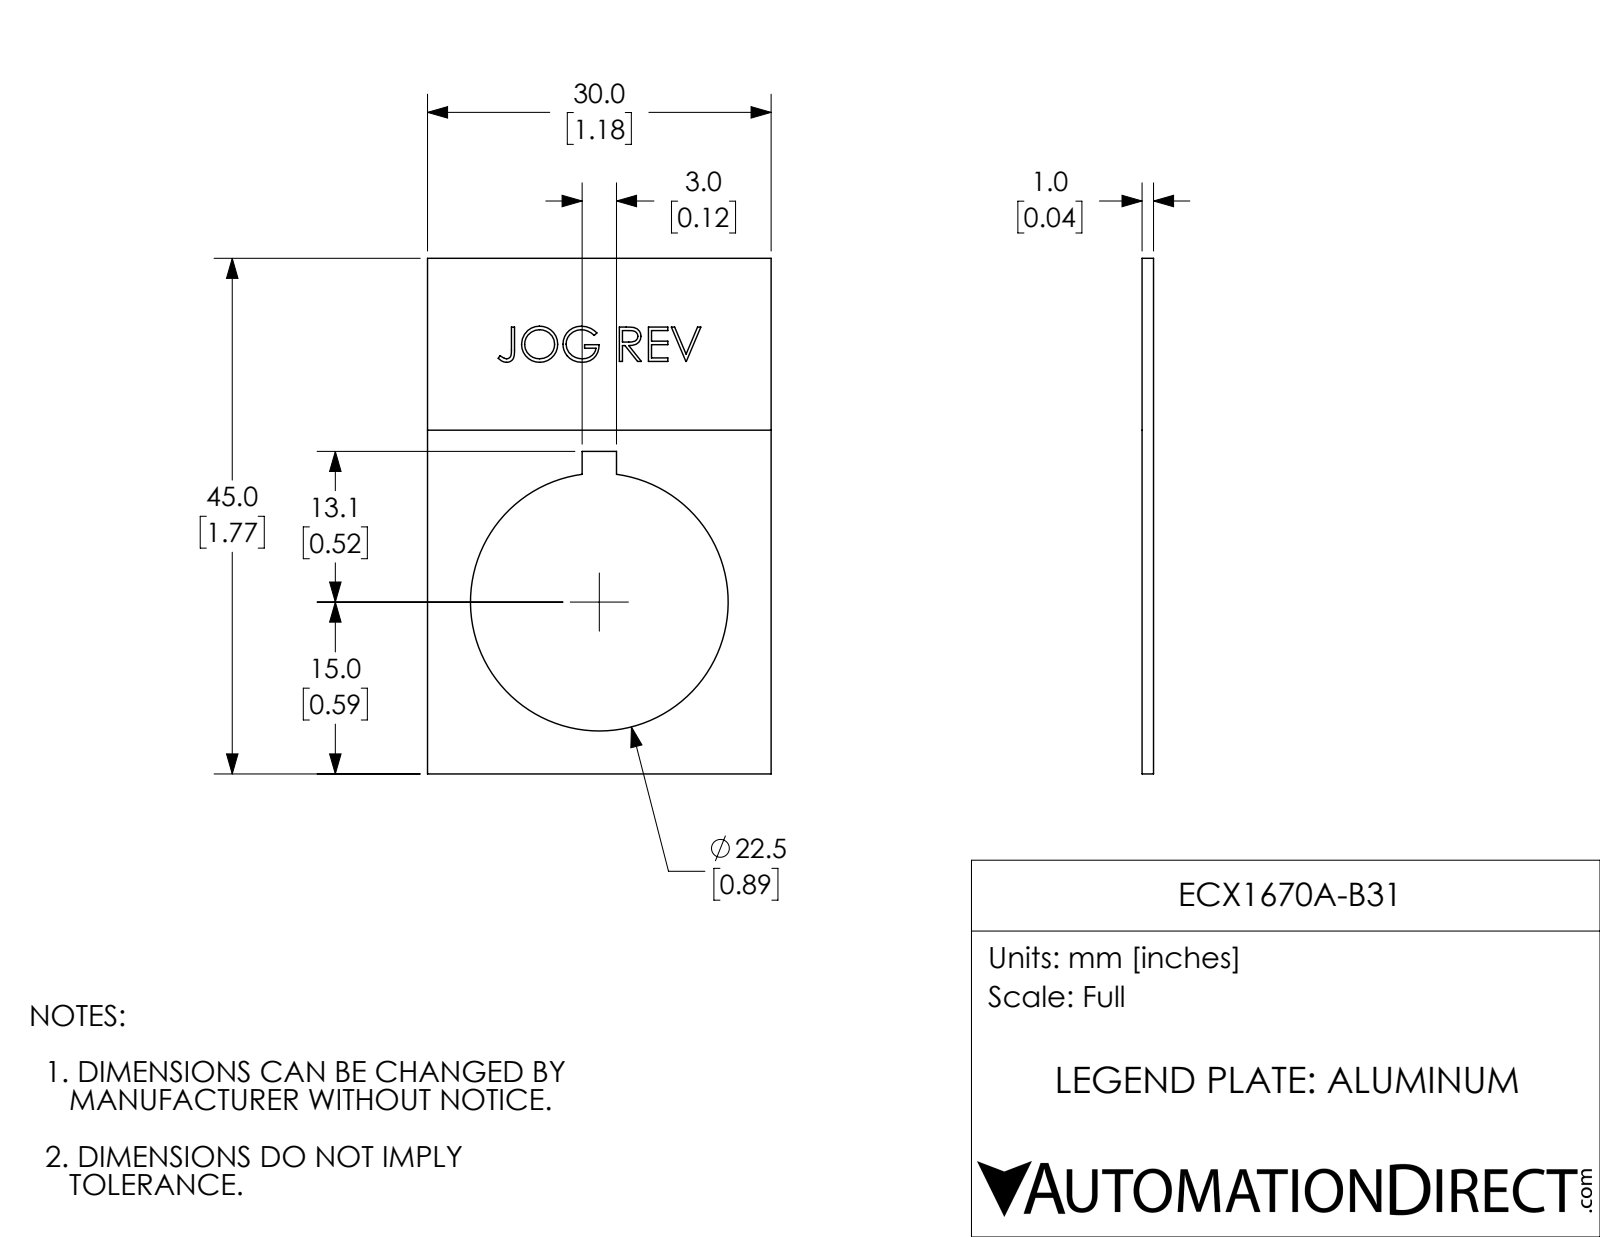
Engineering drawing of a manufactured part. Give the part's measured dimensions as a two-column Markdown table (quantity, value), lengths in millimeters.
| quantity | value |
| --- | --- |
| part name | ECX1670A-B31 |
| STEP written by | SolidWorks 2017 (AUTOMOTIVE_DESIGN) |
| units | millimeters |
| bodies | 1 solid, 86 faces (56 planar, 3 cylindrical, 27 other) |
| overall size | 45 × 30 × 1 |
| volume | 950 mm³ |
| surface area | 2 120 mm² |
| round holes (diameter × count) | 22.5 × 1 |
| main face-to-face distances | 1, 30, 45, 1, 13.5, 16.5, 28.1, 16.8, 3, 0.3 |
